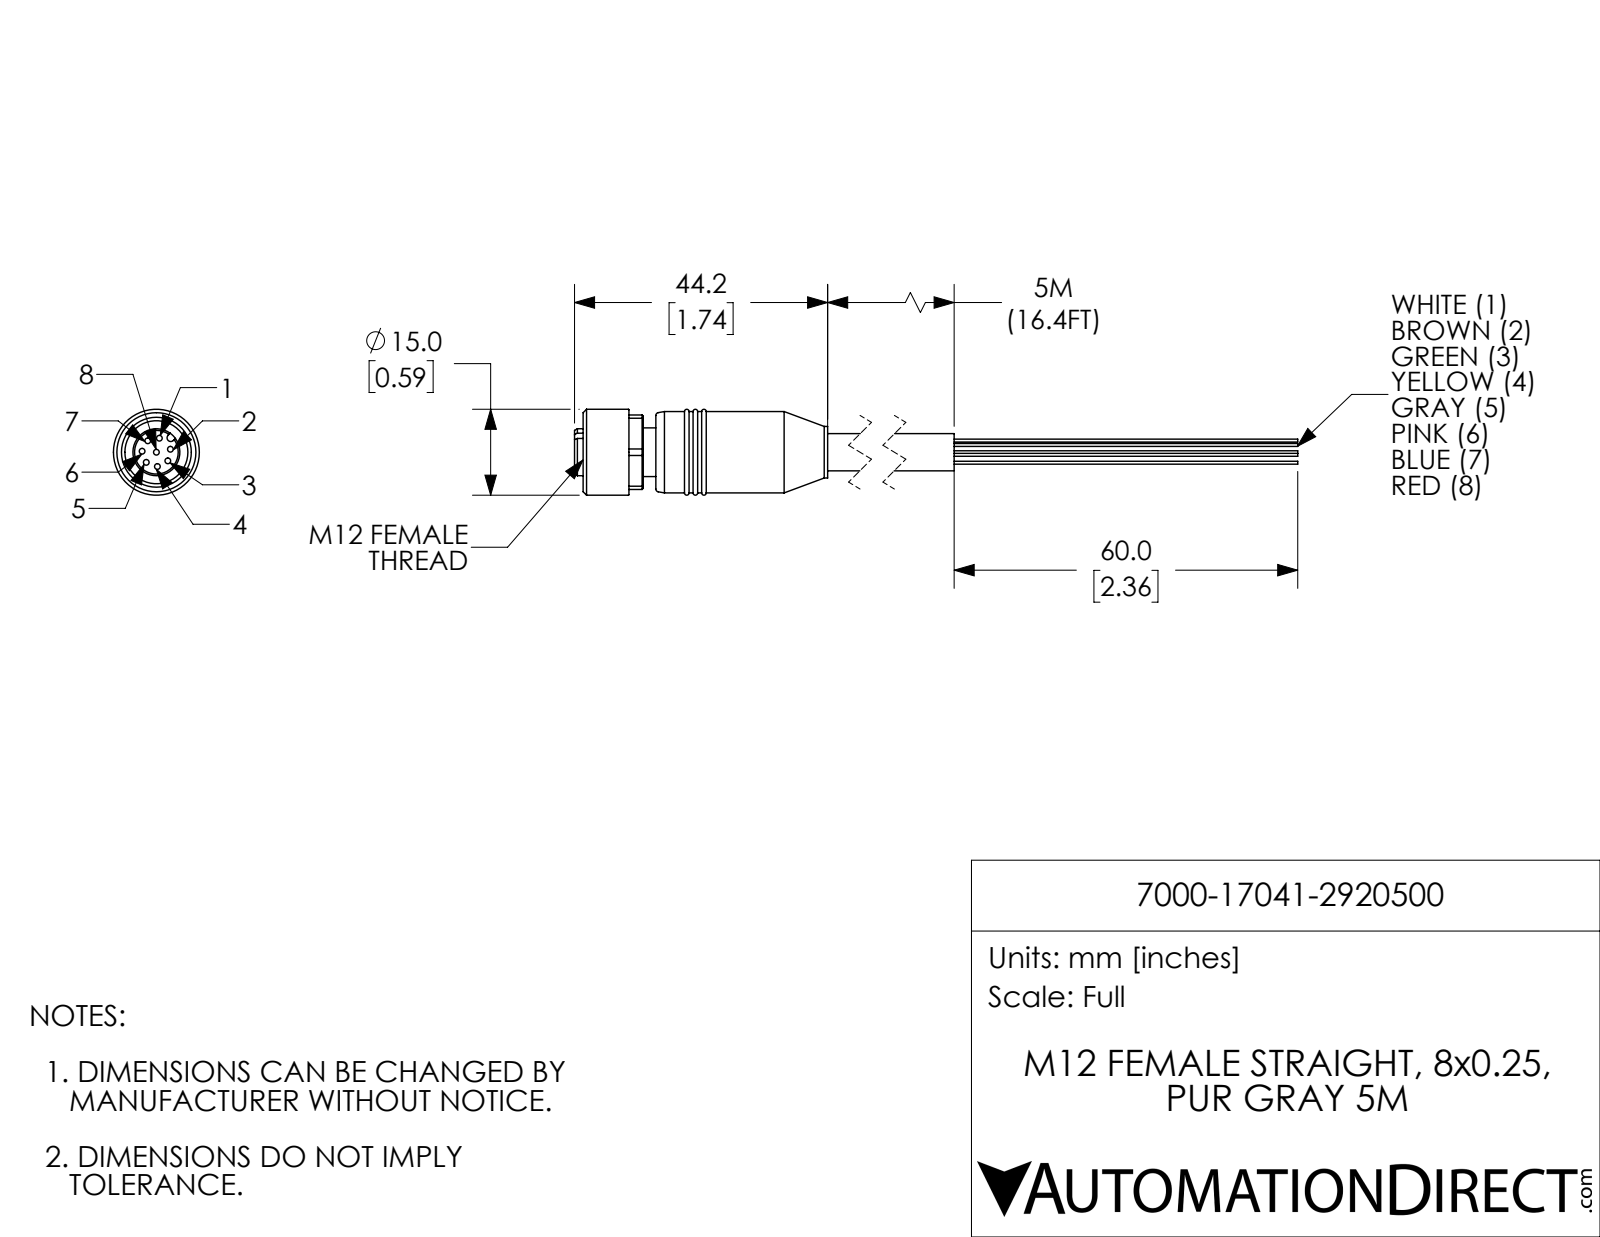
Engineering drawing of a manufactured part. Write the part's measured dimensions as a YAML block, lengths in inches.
part_name: "7000-17041-2920500"
step_written_by: "SolidWorks 2017 (AUTOMOTIVE_DESIGN)"
units: inches
bodies: {solids: 1, faces: 131, planar: 39, cylindrical: 59, other: 33}
overall_size: [4.89, 0.591, 0.591]
volume: 0.41
surface_area: 6.447
round_holes:
  - {diameter: 0.039, count: 8}
  - {diameter: 0.433, count: 1}
round_bosses_or_shafts:
  - {diameter: 0.02, count: 8}
  - {diameter: 0.591, count: 1}
  - {diameter: 0.559, count: 1}
  - {diameter: 0.354, count: 1}
  - {diameter: 0.335, count: 1}
  - {diameter: 0.323, count: 1}
  - {diameter: 0.256, count: 1}
partial_cylinders:
  - {radius: 0.026, count: 1}
  - {radius: 0.283, count: 1}
face_to_face_distances: [0.087, 0.512, 0.118, 0.205, 0.354, 0.472, 0.559, 0.098, 0.059, 0.295]
hole_center_spacings: [0.098, 0.081, 0.149, 0.195, 0.082, 0.166, 0.189, 0.189]
